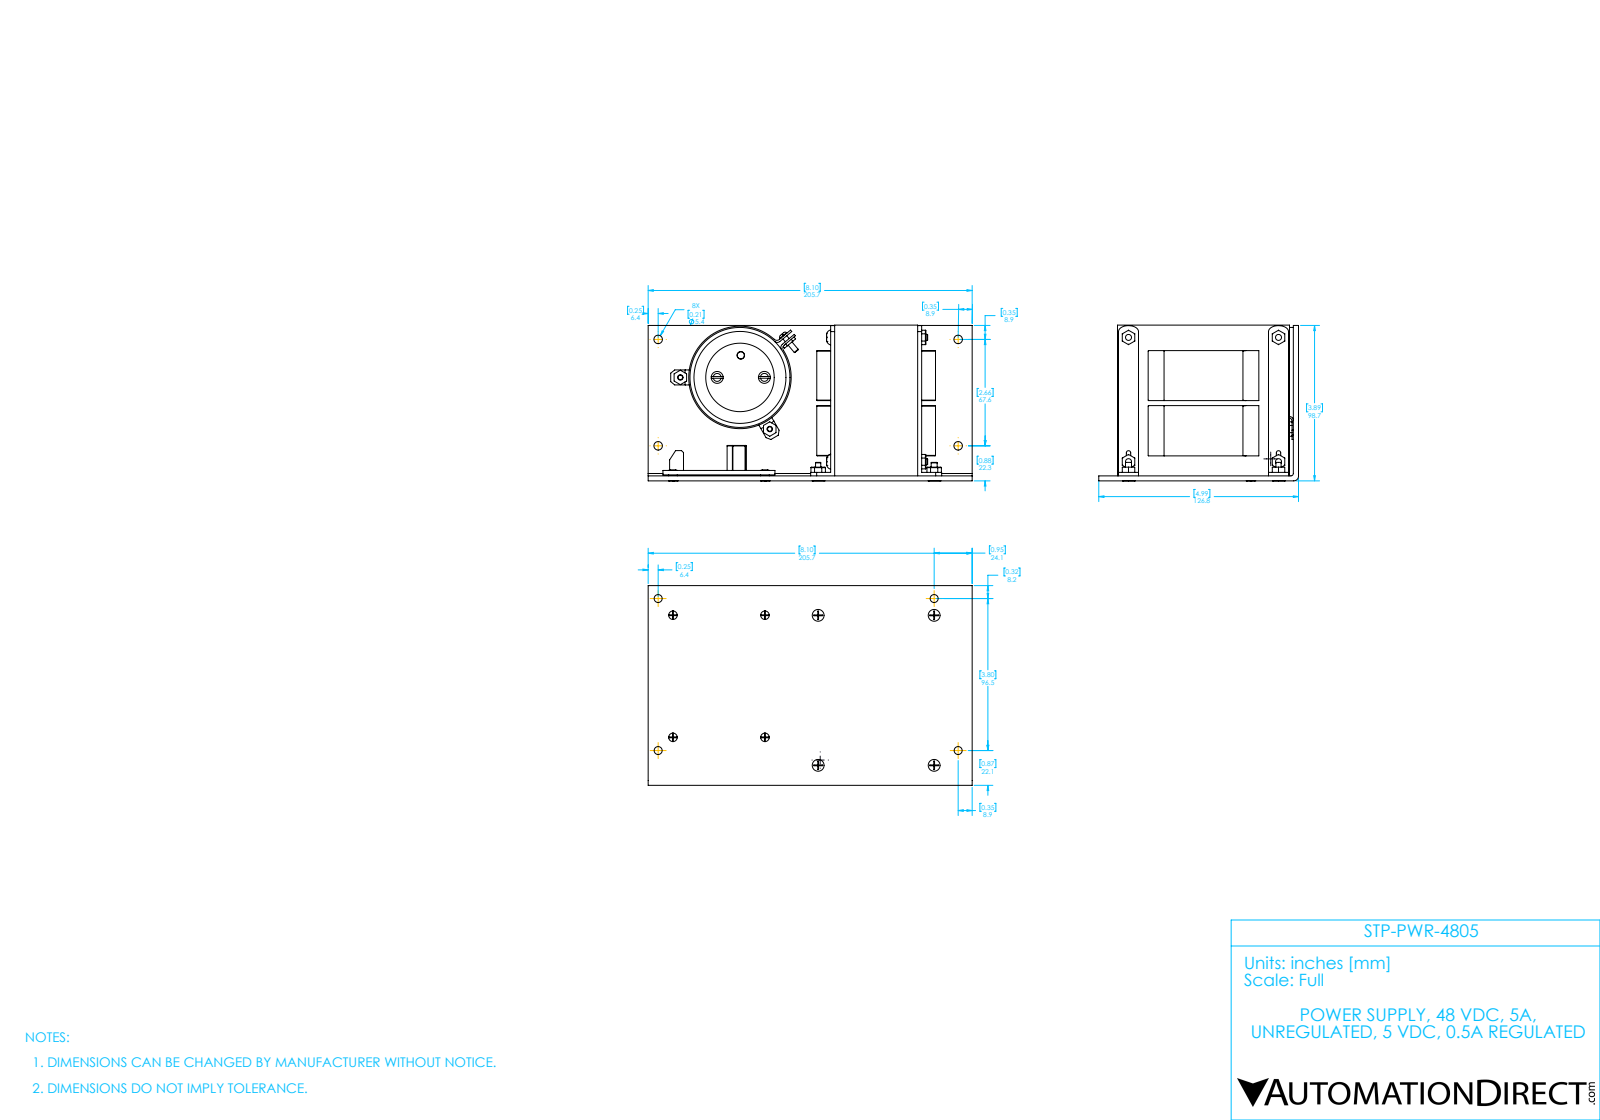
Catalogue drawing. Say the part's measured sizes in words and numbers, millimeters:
The part is named "STP-PWR-4805". Its 3-D file was written by "SolidWorks 2017 (AUTOMOTIVE_DESIGN)". It is 1 solid with 826 faces: 461 planar, 269 cylindrical and 96 other. Overall it measures 205.7 by 126.8 by 98.9 millimeters. Its volume is 1 079 000 cubic millimeters and its surface area 170 400 square millimeters. Round holes: 7 of diameter 2.7, 4 of diameter 5.1, 4 of diameter 5.4, 1 of diameter 3.5. Round bosses or shafts: 5 of diameter 5.4, 5 of diameter 3.8, 4 of diameter 7.5, 3 of diameter 3.3, 2 of diameter 7.6, 2 of diameter 3.5, 2 of diameter 3.1, 2 of diameter 2.7. Partial cylindrical surfaces (rounded edges, fillets, slot ends): 39 of radius 0.3, 16 of radius 0.3, 4 of radius 1.4, 4 of radius 2.5, 4 of radius 2.7, 4 of radius 2.7, 4 of radius 10.9, 1 of radius 1.5. The main face-to-face distances are 3.2, 3.3, 0.6, 3.8, 11.4, 64.1, 6.6, 3.5, 2.8, 98.9. The hole center spacings are 6.1, 190.5, 27.9, 29.1, 57.1, 67.6, 202.1, 6.1.
